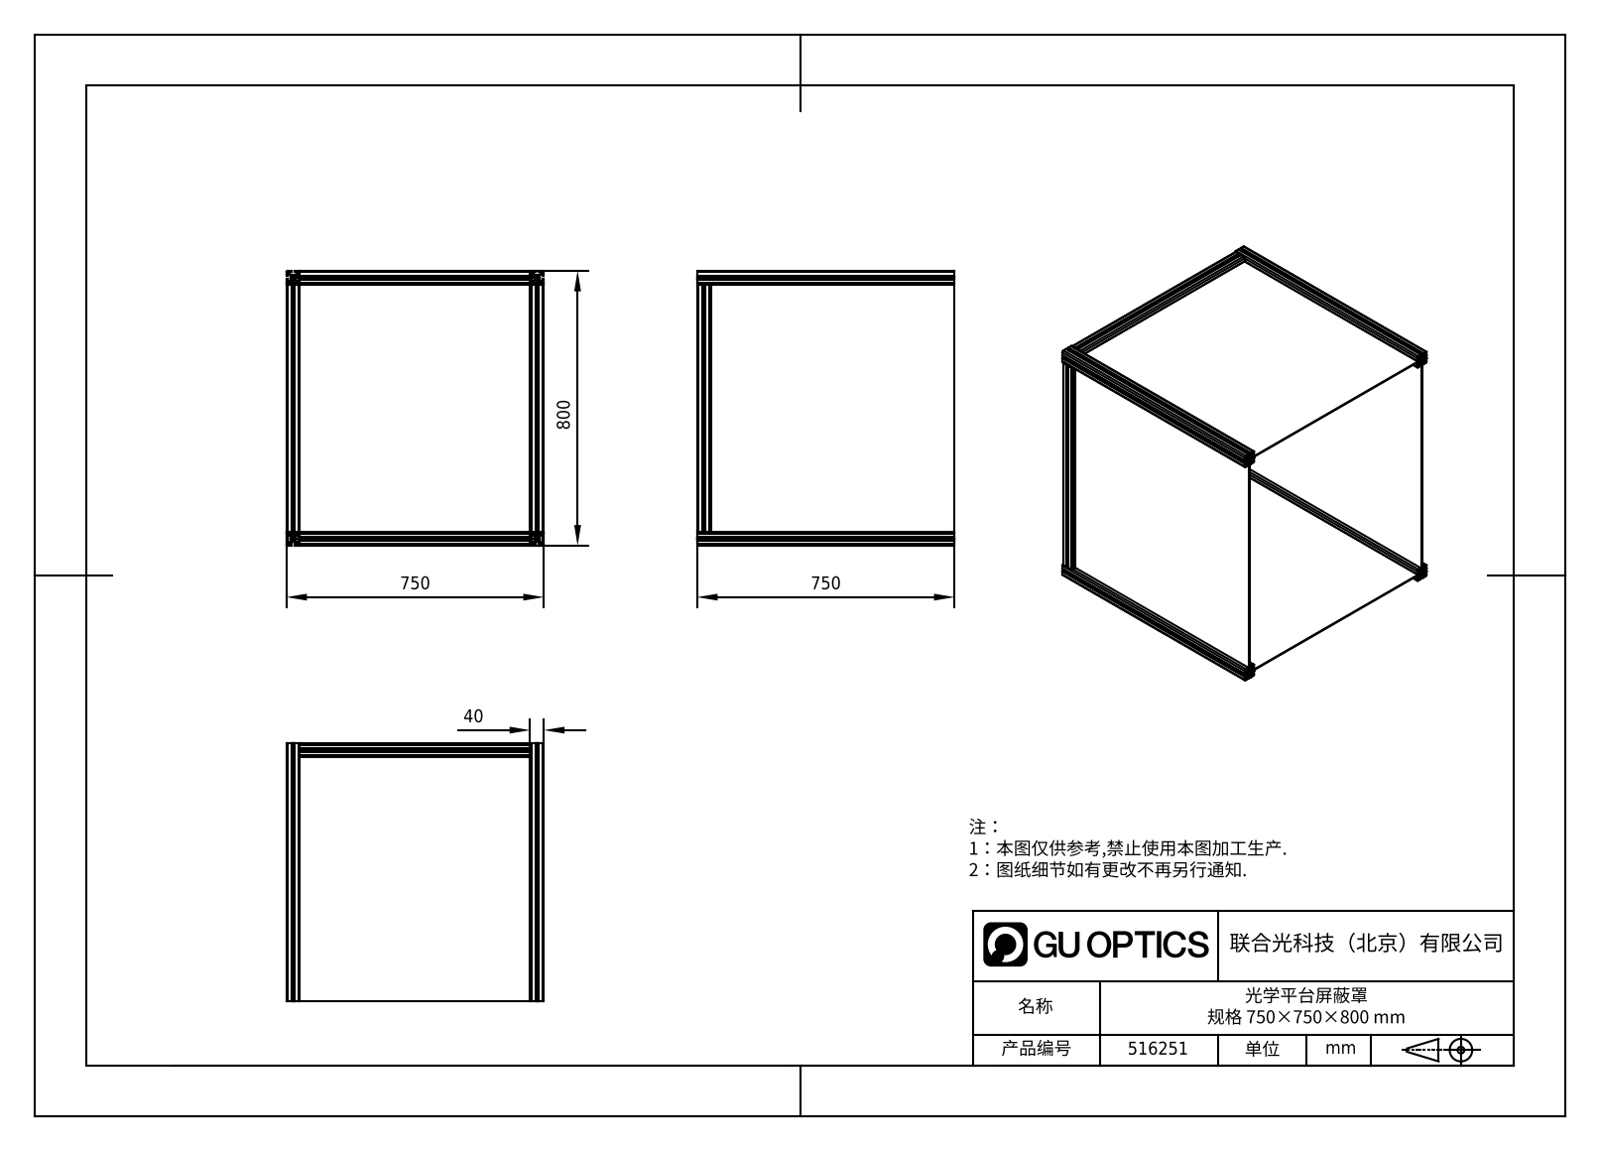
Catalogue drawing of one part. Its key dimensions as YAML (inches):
part_name: "光学平台屏蔽罩边框_670; 516251; 光学平台屏蔽罩面板_694_744; 光学平台屏蔽罩边框_720 (+3 more)"
step_written_by: "SolidWorks 2020 (CONFIG_CONTROL_DESIGN)"
units: inches
bodies: {solids: 13, faces: 1230, planar: 950, cylindrical: 280, other: 0}
overall_size: [31.496, 29.528, 29.528]
volume: 527.7
surface_area: 12510
partial_cylinders:
  - {radius: 0.02, count: 64}
  - {radius: 0.039, count: 64}
  - {radius: 0.03, count: 32}
  - {radius: 0.098, count: 32}
  - {radius: 0.177, count: 32}
  - {radius: 0.134, count: 8}
face_to_face_distances: [0.079, 27.953, 29.921, 28.031, 27.874, 30, 29.843, 0.748, 0.827, 0.504]
